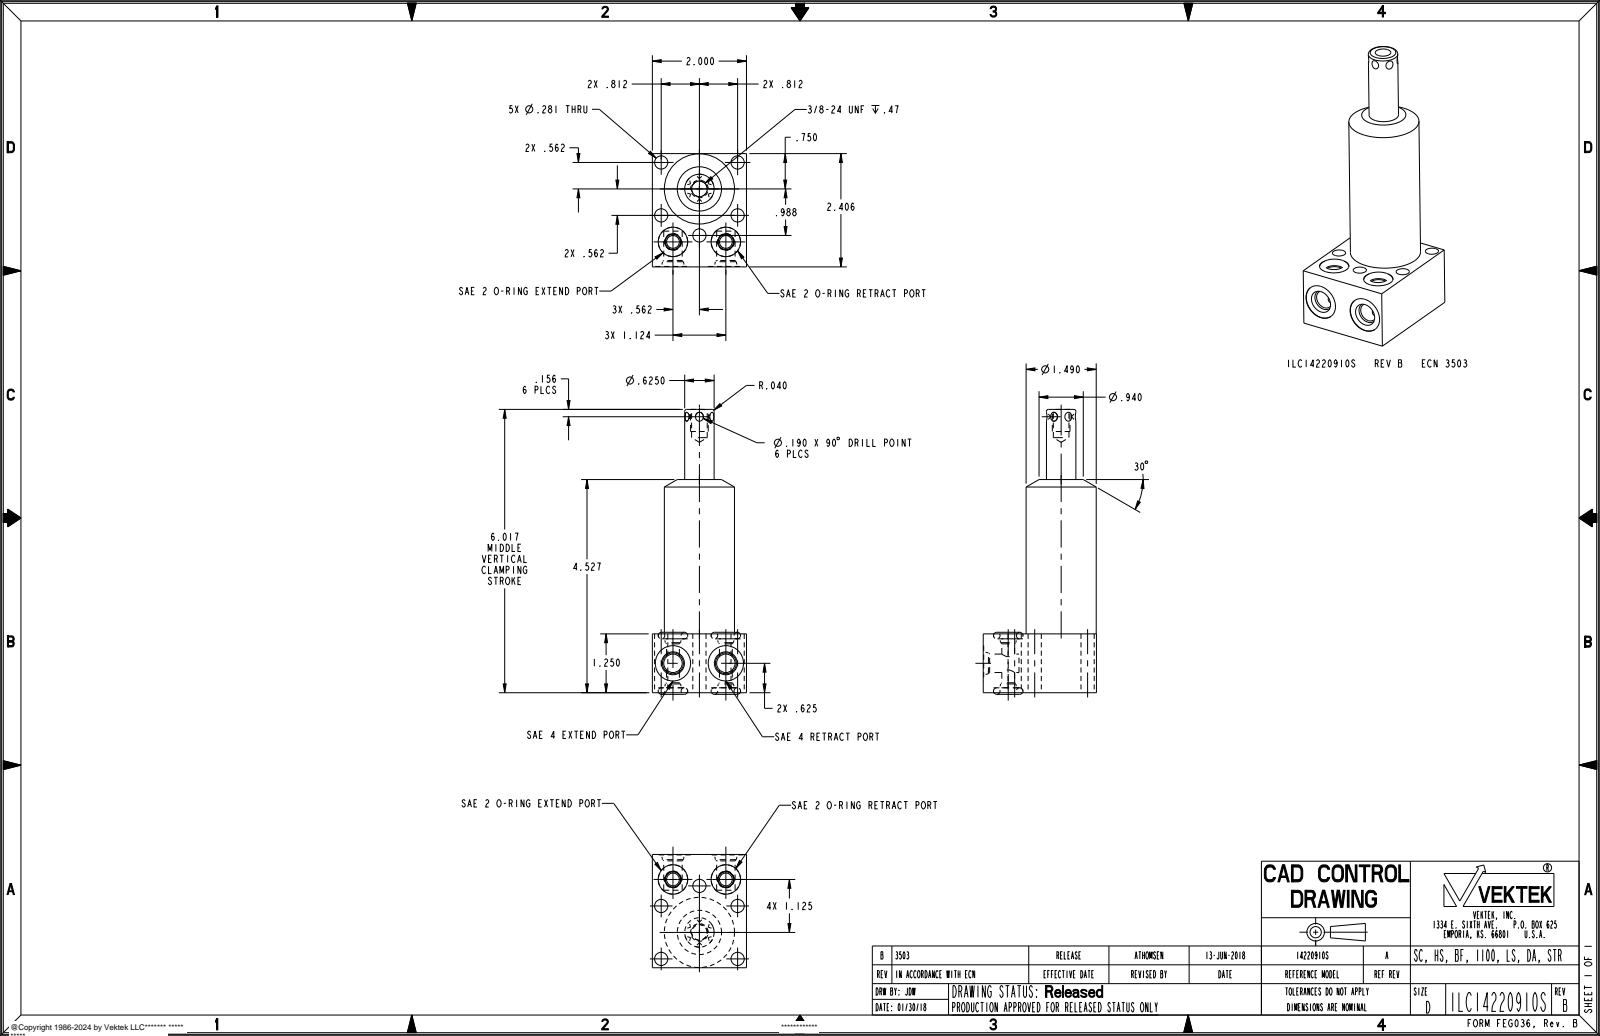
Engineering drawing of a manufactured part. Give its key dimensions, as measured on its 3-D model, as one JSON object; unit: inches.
{"part_name": "ILC14220910S", "step_written_by": "PRO/ENGINEER BY PARAMETRIC TECHNOLOGY CORPORATION, 2013320 (AUTOMOTIVE_DESIGN)", "units": "inches", "bodies": {"solids": 5, "faces": 117, "planar": 17, "cylindrical": 42, "other": 58}, "overall_size": [6.051, 2.406, 2], "volume_in3": 11.32, "surface_area_in2": 50.48, "round_holes": [[0.281, 5], [0.272, 2], [0.392, 2], [0.625, 2], [0.75, 2], [0.332, 1]], "round_bosses_or_shafts": [[1.49, 1], [0.625, 1], [0.375, 1]], "face_to_face_distances": [2, 1.25, 2.406, 0.105, 1.145, 2.396, 1.04, 4.527, 4.422, 3.382], "hole_center_spacings": [0.987, 1.124, 0.578, 0.616, 0.917, 1.257, 1.485, 1.624]}
